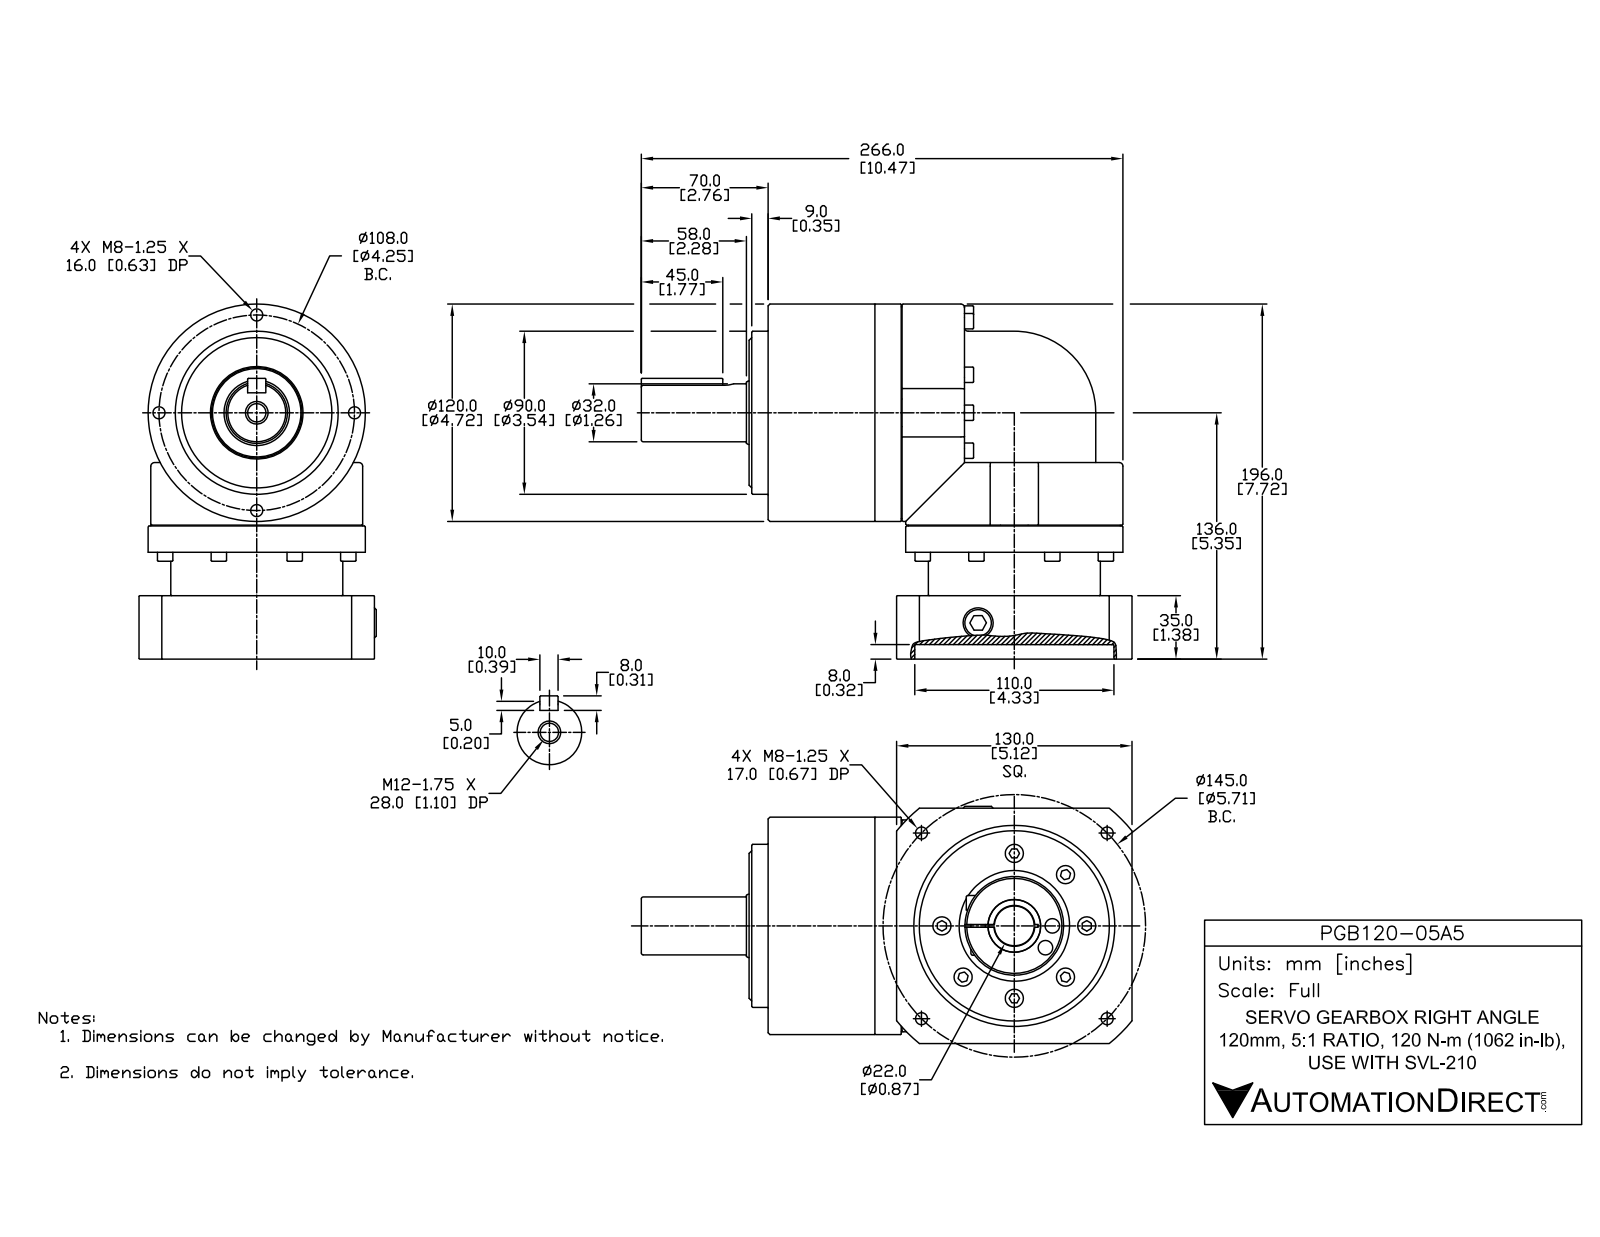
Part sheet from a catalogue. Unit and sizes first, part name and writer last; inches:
Units: inches
Overall size (bounding box): 10.669 × 7.717 × 5.157
Round holes (diameter × count): ⌀0.217 ×8, ⌀0.262 ×8, ⌀0.315 ×2, ⌀0.346 ×1, ⌀0.398 ×1, ⌀0.561 ×1, ⌀0.866 ×1, ⌀2.402 ×1, ⌀4.134 ×1, ⌀4.331 ×1
Round bosses / shafts (diameter × count): ⌀0.335 ×17, ⌀0.197 ×8, ⌀0.394 ×7, ⌀4.724 ×2, ⌀4.606 ×2, ⌀3.74 ×1, ⌀3.543 ×1, ⌀2.146 ×1
Partial cylindrical surfaces — rounded edges, fillets, slot ends (radius × count): R0.079 ×6, R0.098 ×2, R0.131 ×1, R0.197 ×1, R0.276 ×1, R1.772 ×1, R3.287 ×1
Main face-to-face distances: 1.378, 5.118, 0.236, 1.142, 4.272, 2.323, 0.256, 3.209, 1.181, 0.413
Hole centre spacings: 1.194, 1.65, 2.156, 2.843, 3.048, 3.983, 4.184, 4.916
Volume: 162.6 in³ · Surface area: 287.2 in²
Bodies: 1 solid, 700 faces (305 planar, 174 cylindrical, 221 other)
Part name (STEP PRODUCT): PGB120-05A5
STEP written by: SolidWorks 2014 (AUTOMOTIVE_DESIGN)
